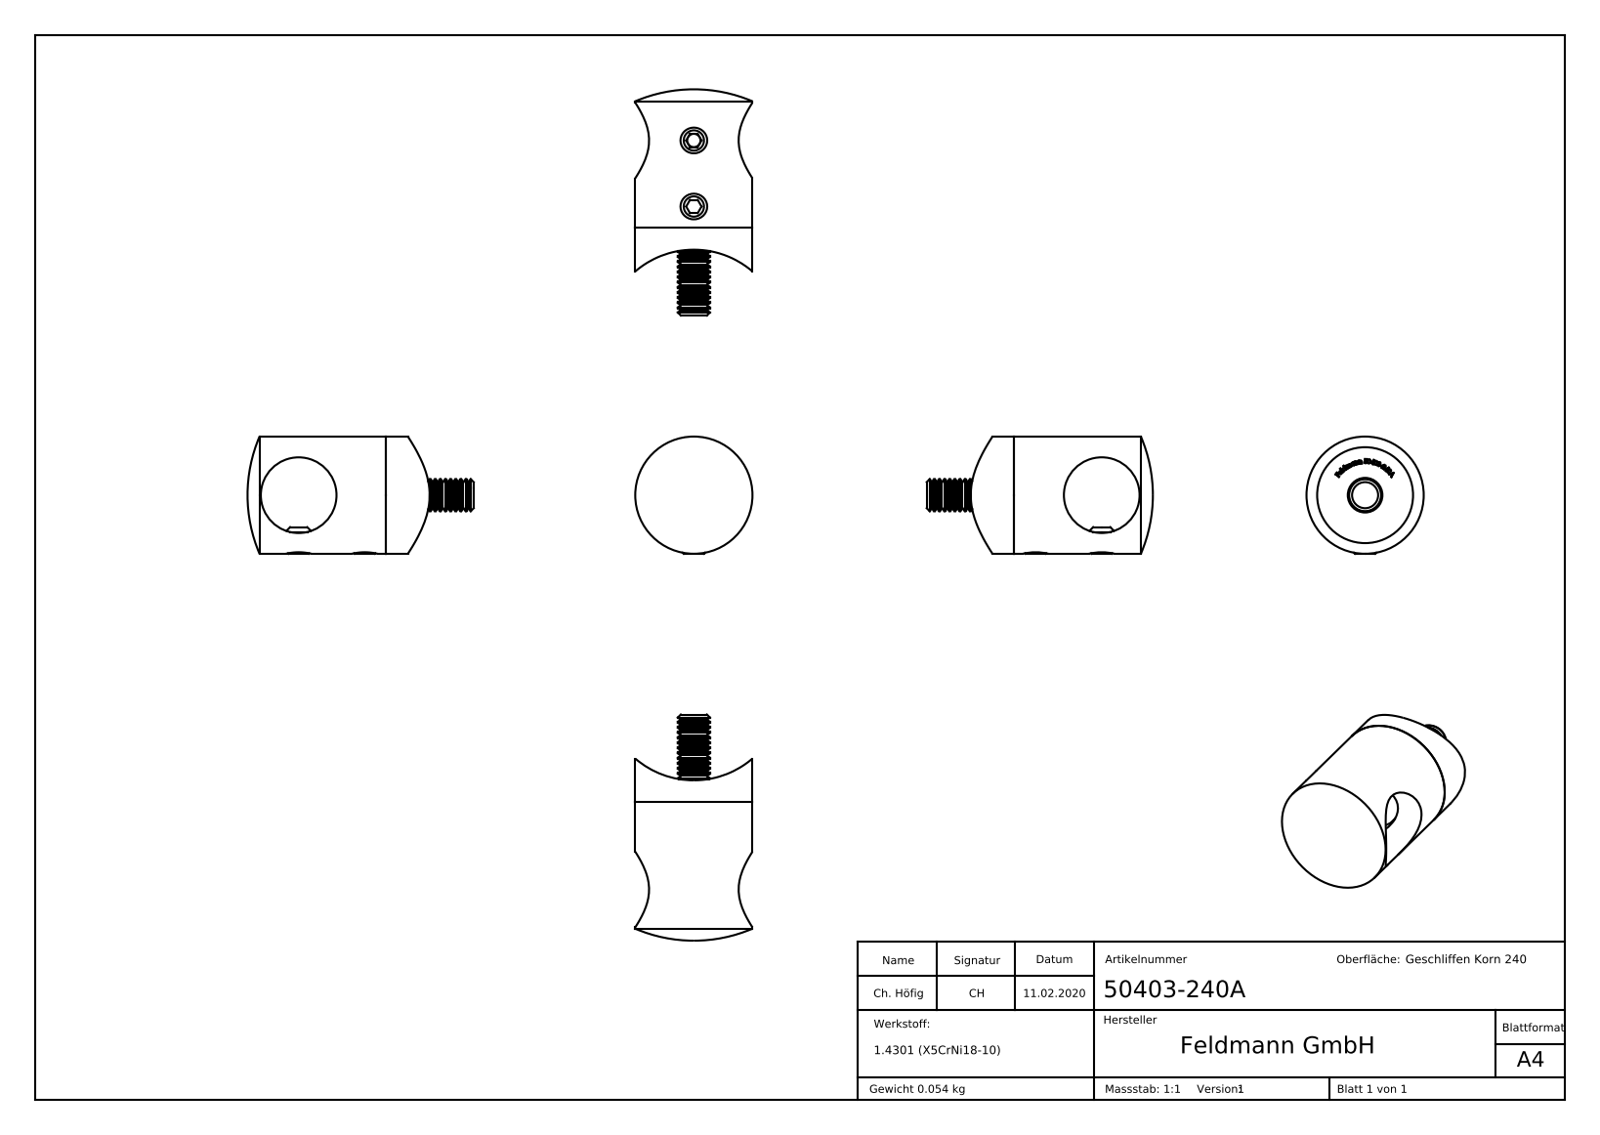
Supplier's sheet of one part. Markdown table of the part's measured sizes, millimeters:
| quantity | value |
| --- | --- |
| part name | socket countersunk head screw_din; 50403-240A; DIN913_DIN 913 M5x5; DIN914 (+7 more) |
| STEP written by | SolidWorks 2015 (CONFIG_CONTROL_DESIGN) |
| units | millimeters |
| bodies | 5 solids, 375 faces (178 planar, 36 cylindrical, 161 other) |
| overall size | 70 × 42.45 × 22 |
| volume | 7 490 mm³ |
| surface area | 6 106 mm² |
| round holes (diameter × count) | 4.2 × 2, 6.5 × 1, 12 × 1, 14.2 × 1, 18 × 1 |
| round bosses / shafts (diameter × count) | 5 × 2, 22 × 1, 11.9 × 1, 11.57 × 1, 6 × 1 |
| partial cylindrical surfaces (radius × count) | 16.85 × 1 |
| main face-to-face distances | 2.1, 10.65, 8.55, 2.5, 9.6, 7.5, 1.05, 14.35, 16.45, 23.95 |
| hole center spacings | 12.4 |
